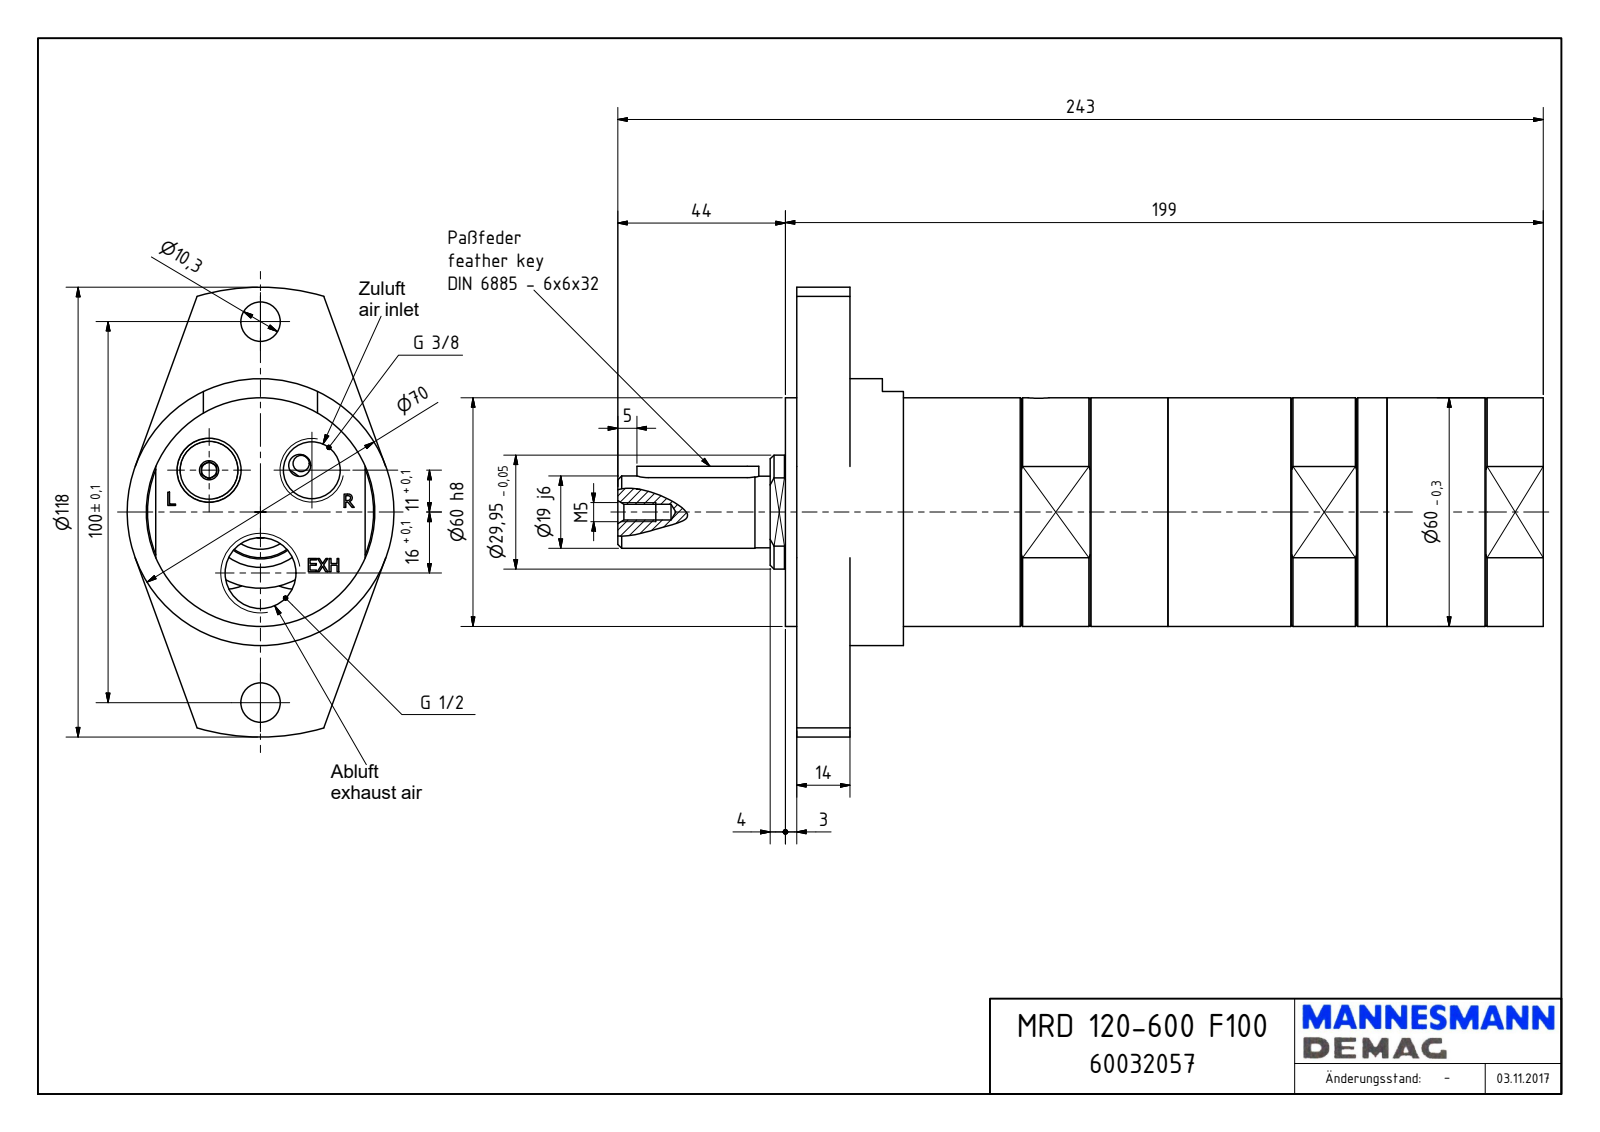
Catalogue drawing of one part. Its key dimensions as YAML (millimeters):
part_name: "MRD 120-600 F100_60032057"
step_written_by: "Autodesk Inventor 2018 (AUTOMOTIVE_DESIGN)"
units: millimeters
bodies: {solids: 1, faces: 511, planar: 224, cylindrical: 243, other: 44}
overall_size: [243, 118, 70]
volume: 618234
surface_area: 65123
round_holes:
  - {diameter: 4, count: 2}
  - {diameter: 10.3, count: 2}
  - {diameter: 14.95, count: 2}
  - {diameter: 1.55, count: 1}
  - {diameter: 4.13, count: 1}
  - {diameter: 5.5, count: 1}
  - {diameter: 18.63, count: 1}
  - {diameter: 35, count: 1}
  - {diameter: 53.38, count: 1}
round_bosses_or_shafts:
  - {diameter: 70, count: 1}
  - {diameter: 60, count: 1}
  - {diameter: 55.18, count: 1}
  - {diameter: 53.18, count: 1}
  - {diameter: 29.95, count: 1}
  - {diameter: 19, count: 1}
  - {diameter: 18.8, count: 1}
  - {diameter: 5, count: 1}
partial_cylinders:
  - {radius: 11.68, count: 94}
  - {radius: 3, count: 2}
  - {radius: 7.5, count: 2}
  - {radius: 8.5, count: 1}
  - {radius: 19.13, count: 1}
  - {radius: 23.5, count: 1}
  - {radius: 24.76, count: 1}
  - {radius: 24.96, count: 1}
face_to_face_distances: [14, 196, 182, 3, 17, 199, 55, 28, 31, 168]
hole_center_spacings: [17.41, 30.19, 41.27, 50, 62.48, 16, 27, 34]
